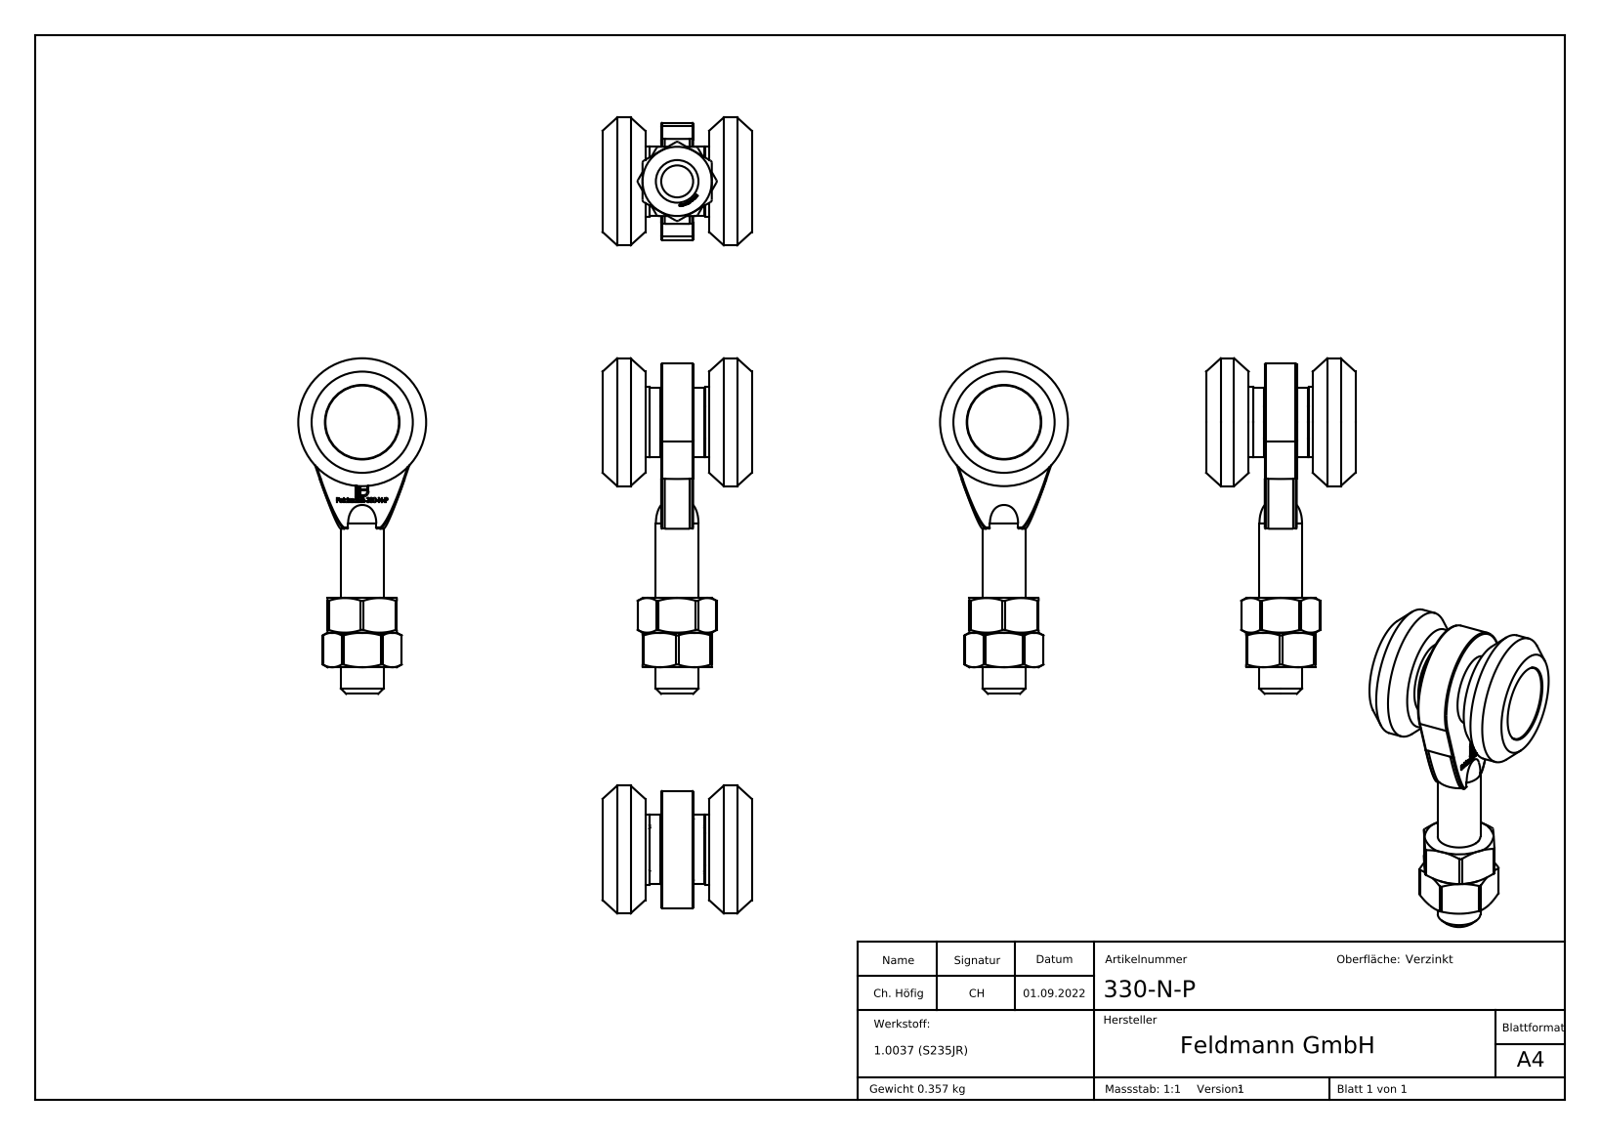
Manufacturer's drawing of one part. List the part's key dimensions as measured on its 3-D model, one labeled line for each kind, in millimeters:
Part name (STEP PRODUCT): 330-N-P; DIN 934 M4-M20_DIN 934 M8; 330-X-X Konfig_330-N-P Teil1
STEP written by: SolidWorks 2018 (CONFIG_CONTROL_DESIGN)
Units: millimetres
Bodies: 7 solids, 818 faces (430 planar, 40 cylindrical, 348 other)
Overall size (bounding box): 63 × 28 × 24
Volume: 12 973 mm³ · Surface area: 7 986 mm²
Round holes (diameter × count): ⌀6.2 ×1, ⌀6.8 ×1, ⌀14 ×1
Round bosses / shafts (diameter × count): ⌀24 ×1, ⌀13.8 ×1, ⌀13.2 ×1, ⌀13 ×1, ⌀8 ×1, ⌀6.1 ×1
Partial cylindrical surfaces — rounded edges, fillets, slot ends (radius × count): R0.5 ×12, R0.2 ×6, R11 ×1
Main face-to-face distances: 7.8, 8, 19, 0.8, 10, 0.9, 19.1, 16.1, 6, 7.9
